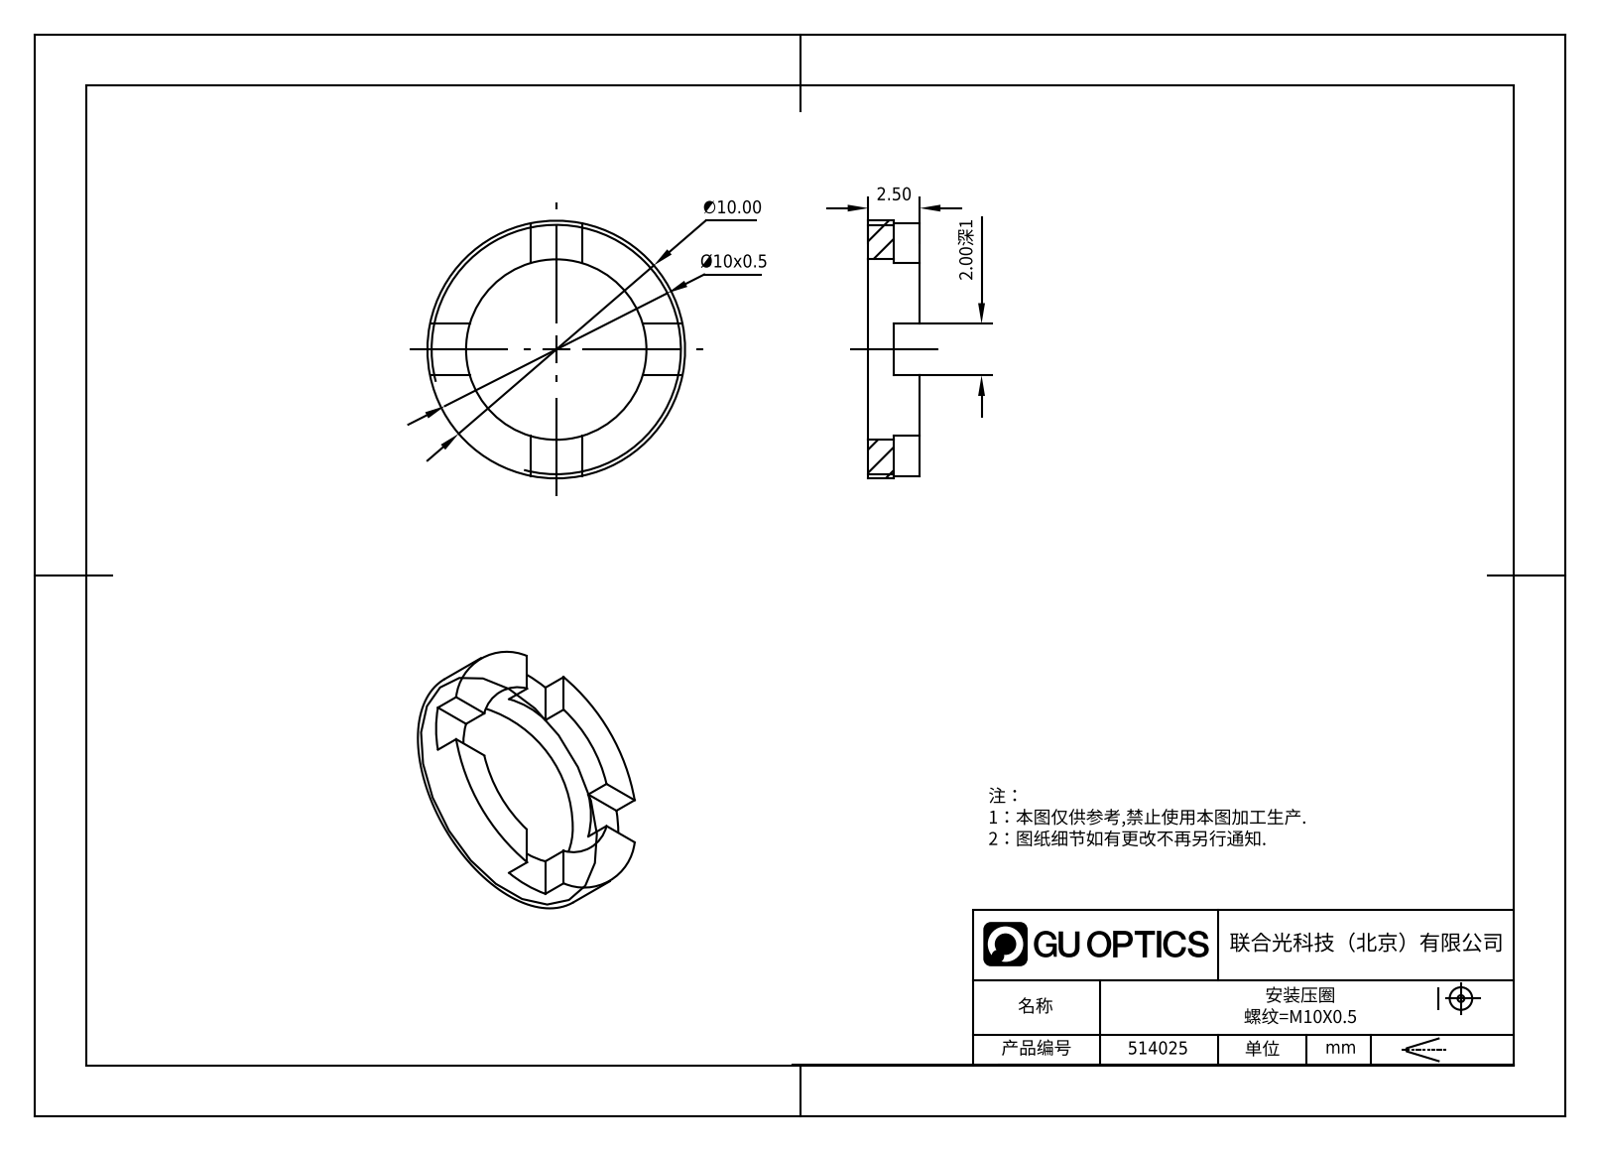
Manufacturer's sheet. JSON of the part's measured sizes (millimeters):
{"part_name": "514025", "step_written_by": "SolidWorks 2020 (CONFIG_CONTROL_DESIGN)", "units": "millimeters", "bodies": {"solids": 1, "faces": 21, "planar": 17, "cylindrical": 4, "other": 0}, "overall_size": [10, 10, 2], "volume_mm3": 68, "surface_area_mm2": 183, "round_holes": [[7, 1]], "round_bosses_or_shafts": [[10, 1]], "face_to_face_distances": [2, 1]}
